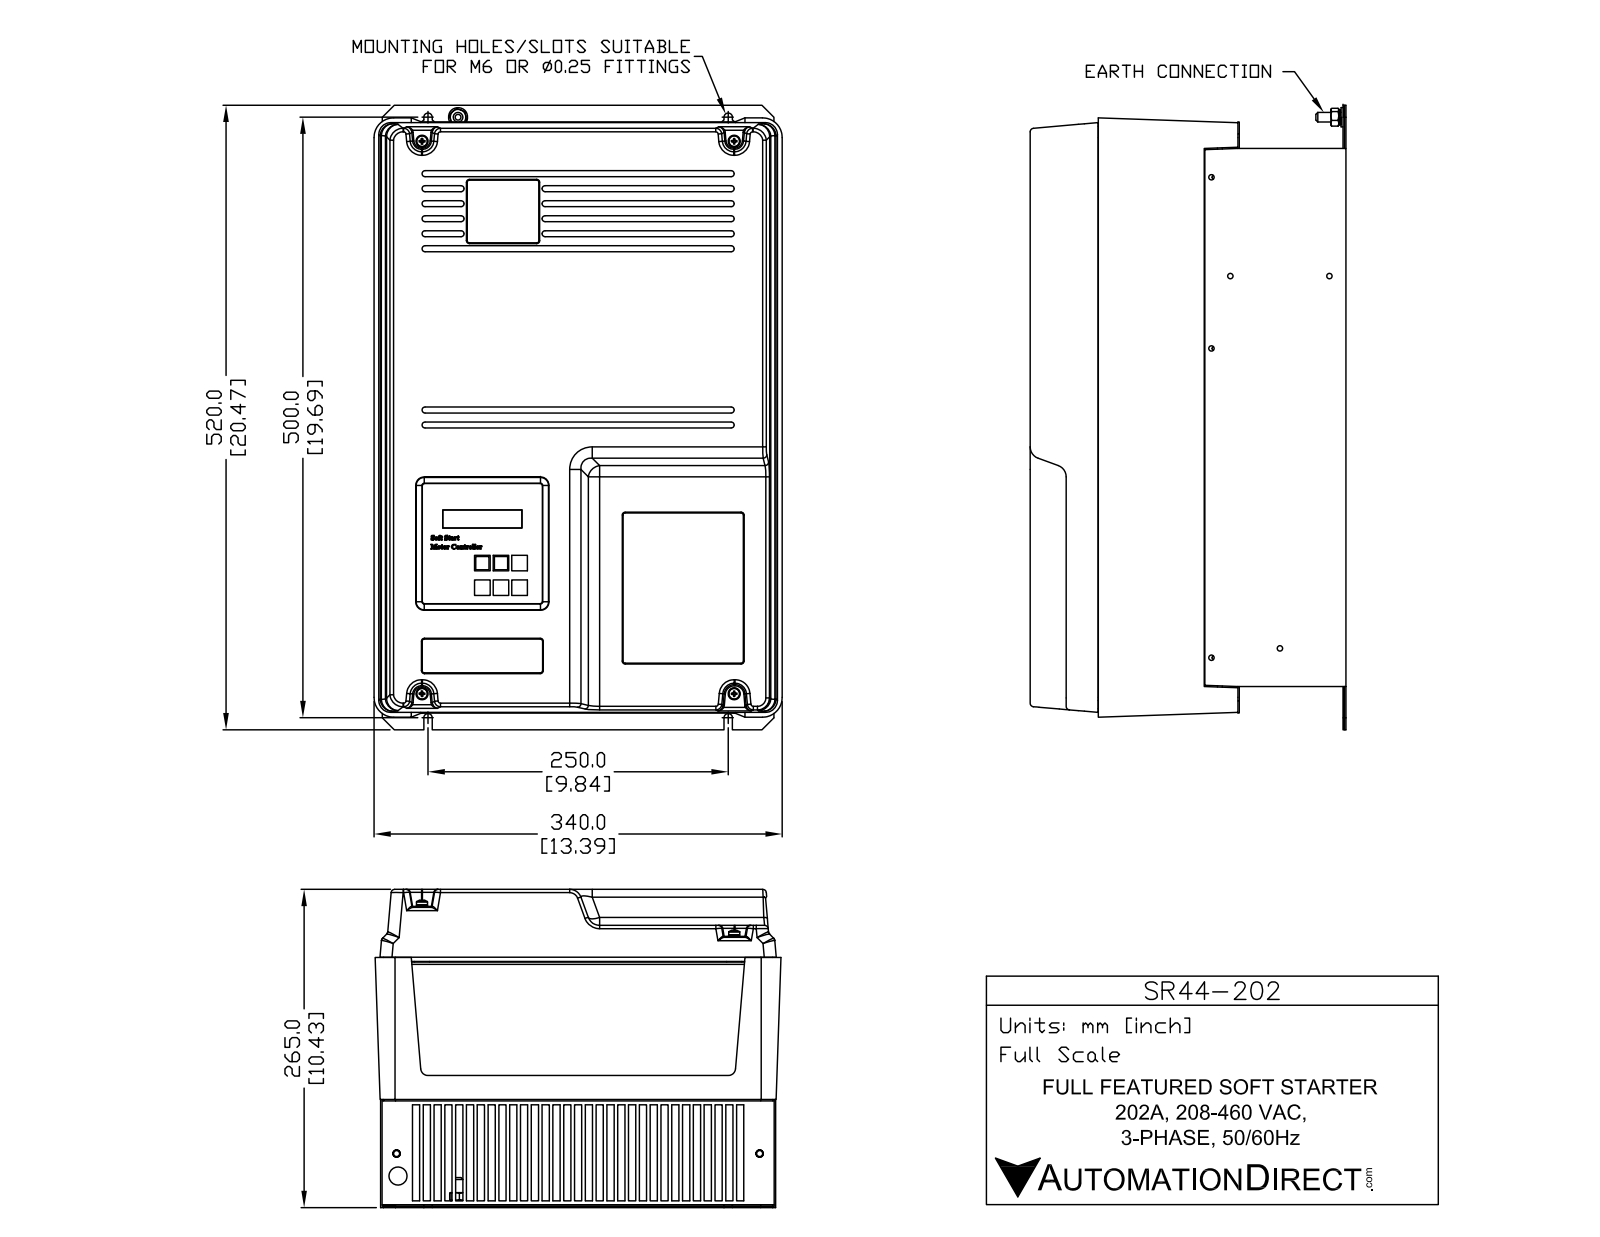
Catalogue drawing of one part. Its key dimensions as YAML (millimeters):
part_name: "SR44-202"
step_written_by: "SolidWorks 2013 (AUTOMOTIVE_DESIGN)"
units: millimeters
bodies: {solids: 1, faces: 828, planar: 518, cylindrical: 144, other: 166}
overall_size: [520, 337.91, 263]
volume: 38650000
surface_area: 1324000
round_holes:
  - {diameter: 13, count: 2}
round_bosses_or_shafts:
  - {diameter: 10, count: 4}
  - {diameter: 16, count: 1}
  - {diameter: 8, count: 1}
partial_cylinders:
  - {radius: 5, count: 31}
  - {radius: 3, count: 16}
  - {radius: 2.4, count: 12}
  - {radius: 1.5, count: 8}
  - {radius: 15, count: 8}
  - {radius: 2, count: 6}
  - {radius: 3.5, count: 4}
  - {radius: 10, count: 2}
face_to_face_distances: [8.9, 17.8, 26.7, 35.6, 263, 5.75, 14.65, 44.5, 3.15, 23.55]
hole_center_spacings: [250]
